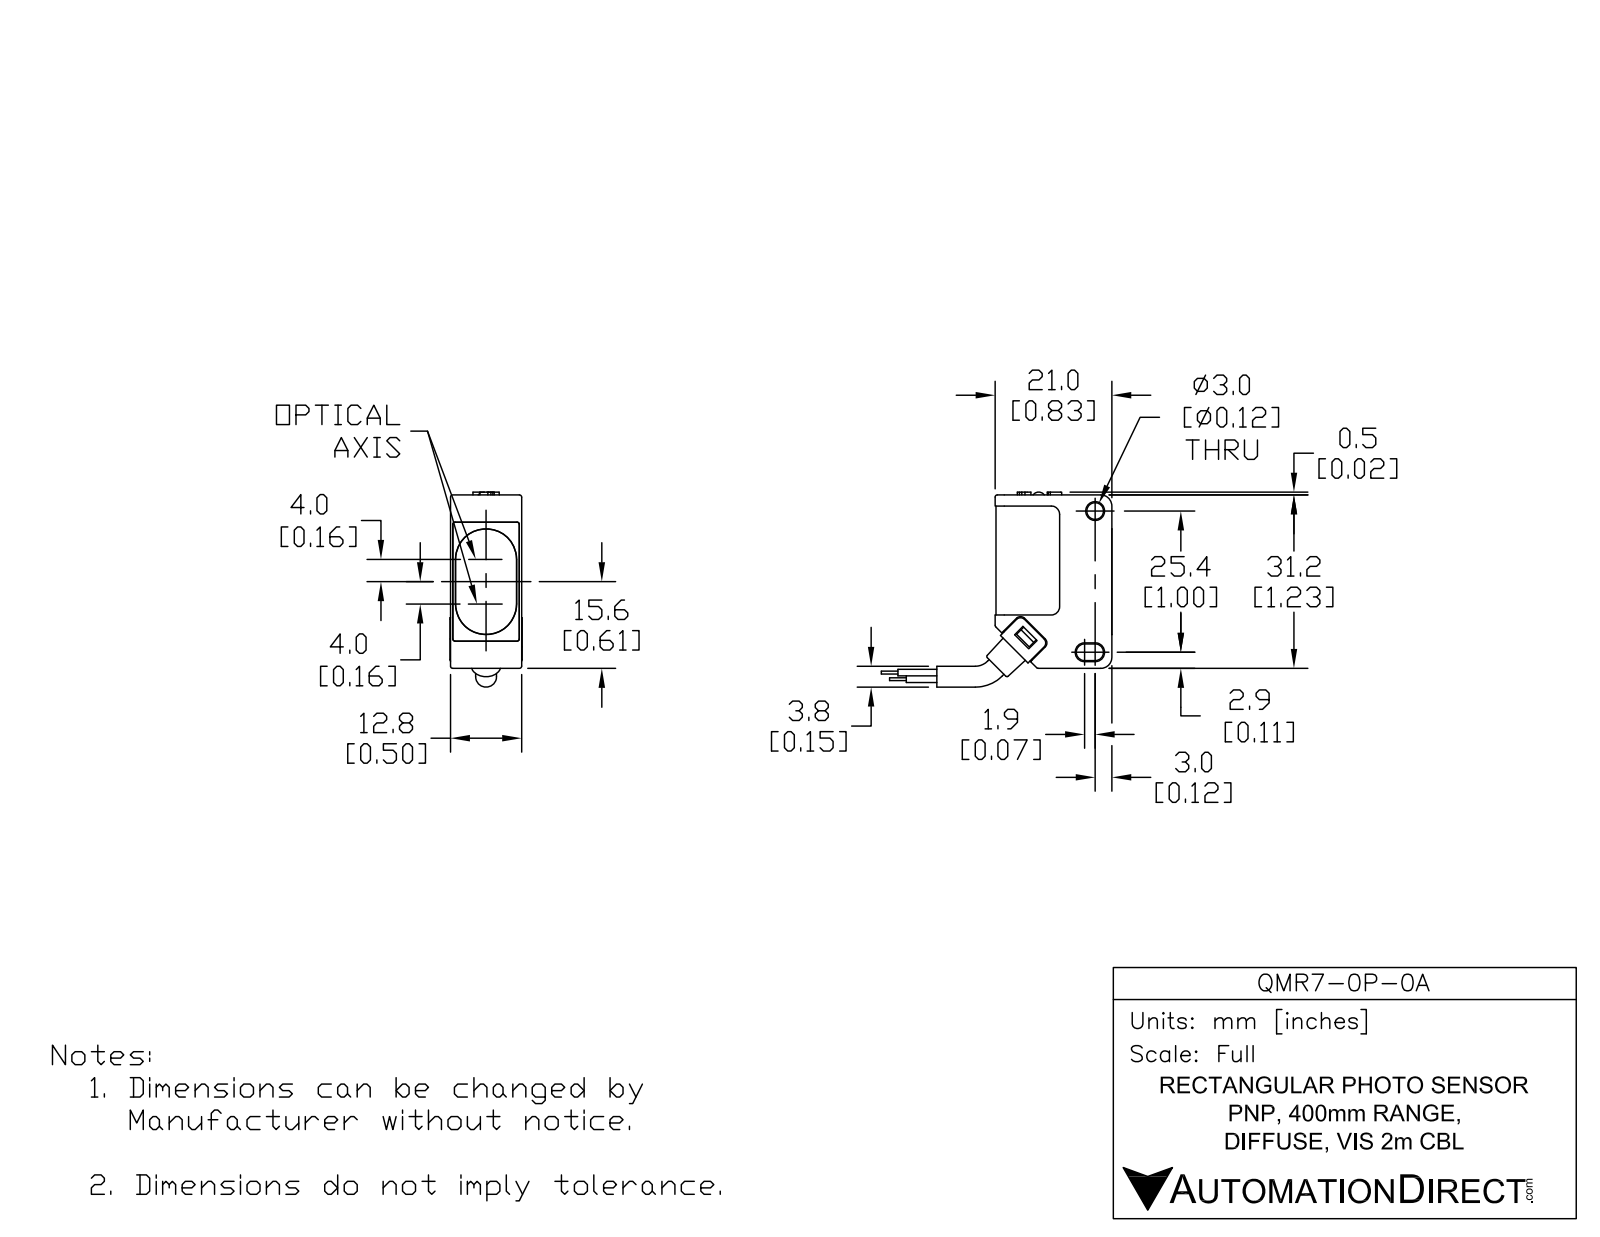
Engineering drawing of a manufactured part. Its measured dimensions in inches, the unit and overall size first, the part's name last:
Units: inches
Overall size (bounding box): 3.193 × 1.032 × 0.512
Round holes (diameter × count): ⌀0.118 ×3, ⌀0.148 ×1, ⌀0.224 ×1, ⌀0.283 ×1
Round bosses / shafts (diameter × count): ⌀0.138 ×2
Partial cylindrical surfaces — rounded edges, fillets, slot ends (radius × count): R0.016 ×13, R0.02 ×10, R0.039 ×8, R0.059 ×6, R0.024 ×4, R0.006 ×2, R0.035 ×2, R0.044 ×2
Main face-to-face distances: 0.02, 0.498, 0.059, 0.016, 0.504, 0.138, 0.488, 0.079, 0.482, 0.492
Hole centre spacings: 0.205
Volume: 0.47 in³ · Surface area: 8.375 in²
Bodies: 9 solids, 258 faces (134 planar, 100 cylindrical, 24 other)
Part name (STEP PRODUCT): QMR7-0P-0A
STEP written by: SolidWorks 2017 (AUTOMOTIVE_DESIGN)
